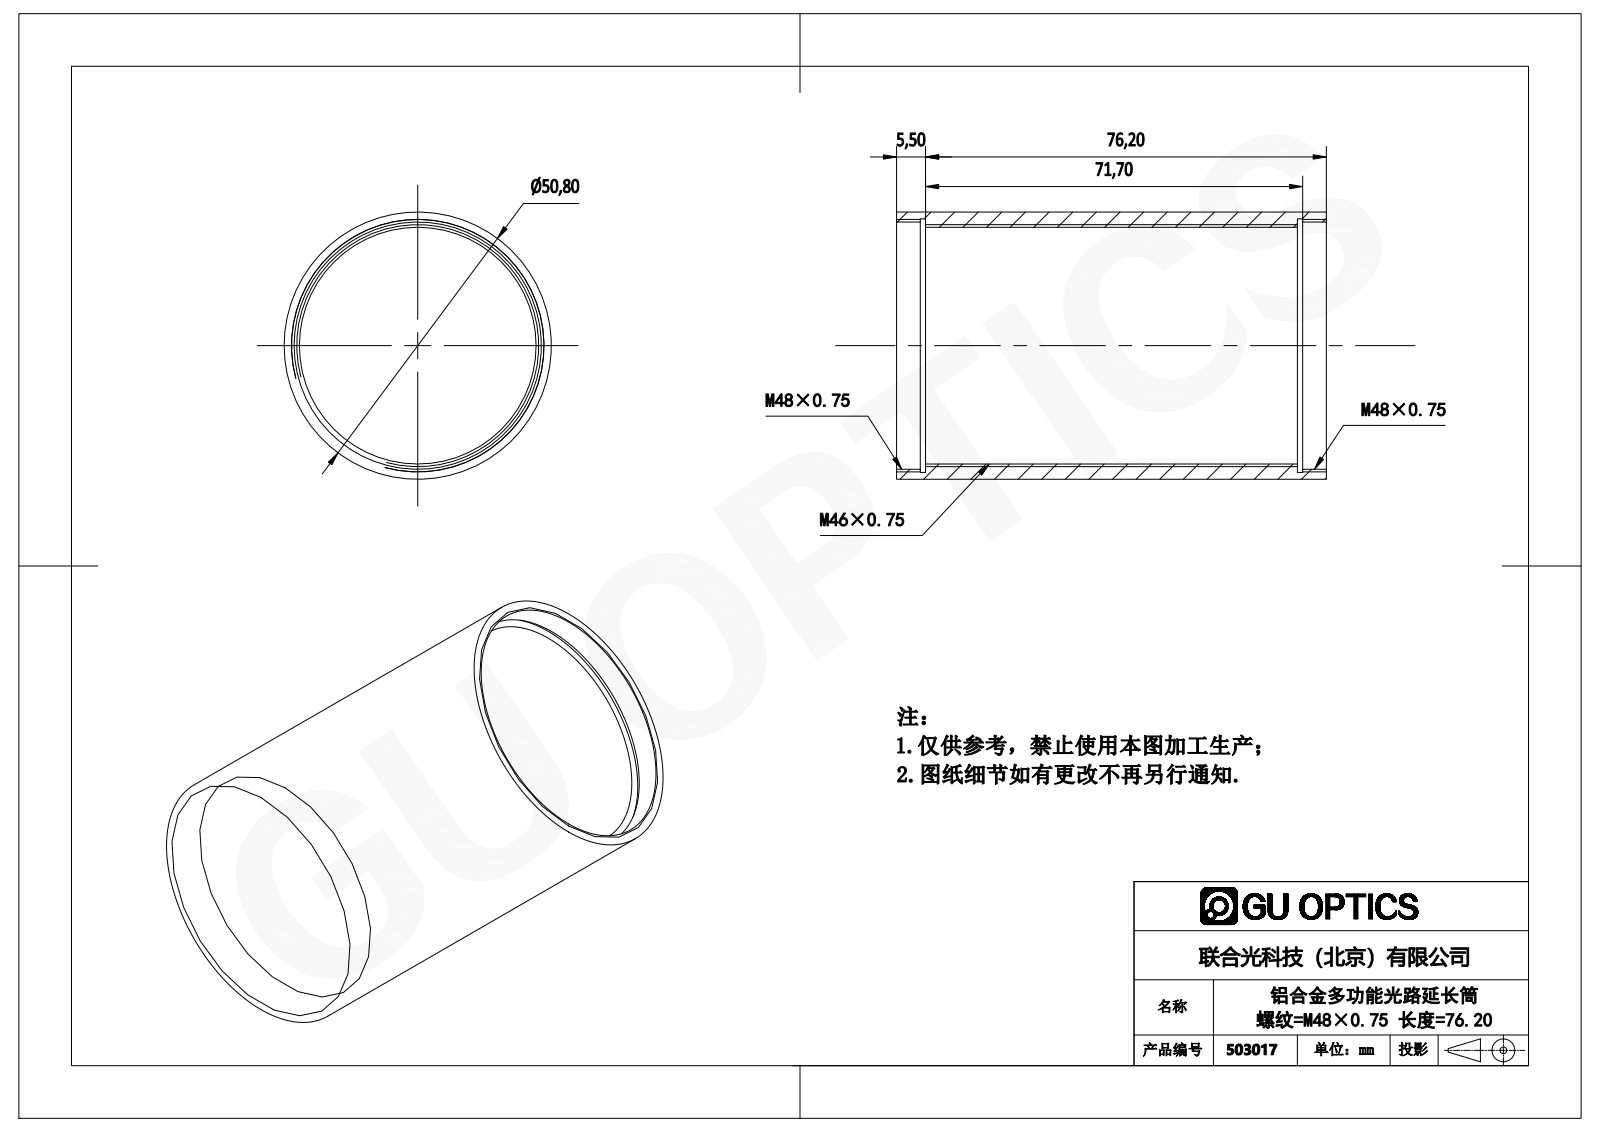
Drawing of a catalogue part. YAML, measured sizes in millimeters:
part_name: "503017"
step_written_by: "SolidWorks 2016 (AUTOMOTIVE_DESIGN)"
units: millimeters
bodies: {solids: 1, faces: 18, planar: 6, cylindrical: 12, other: 0}
overall_size: [81.7, 50.8, 50.8]
volume: 33885
surface_area: 25897
round_holes:
  - {diameter: 45, count: 1}
  - {diameter: 47, count: 1}
  - {diameter: 48.2, count: 1}
round_bosses_or_shafts:
  - {diameter: 50.8, count: 1}
face_to_face_distances: [5.5, 76.2, 81.7, 70.7, 4.5, 77.2, 1, 71.7, 72.7]
